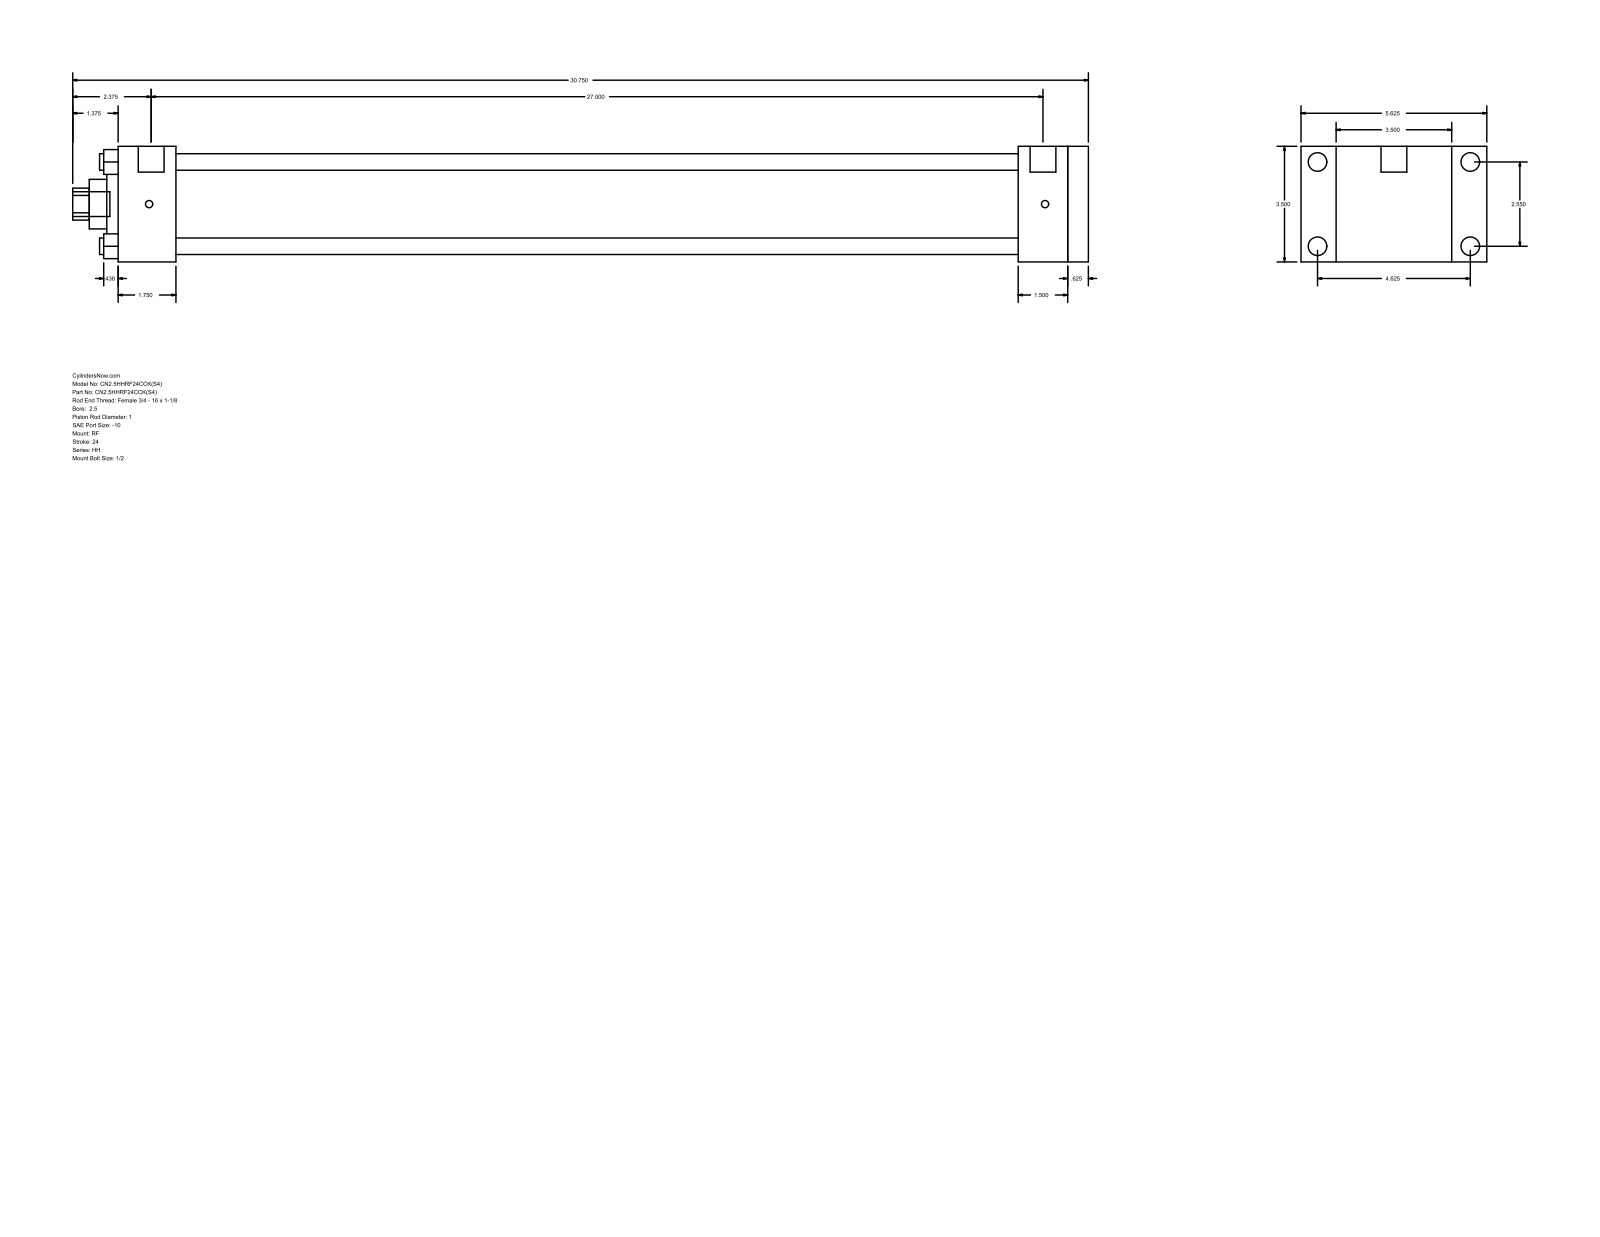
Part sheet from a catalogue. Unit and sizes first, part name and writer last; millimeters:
Units: millimetres
Overall size (bounding box): 781.05 × 142.88 × 88.9
Round holes (diameter × count): ⌀12.7 ×4, ⌀25.4 ×1, ⌀38.1 ×1, ⌀60.33 ×1, ⌀73.03 ×1
Round bosses / shafts (diameter × count): ⌀14.3 ×4, ⌀5.56 ×4, ⌀19.84 ×2, ⌀19.05 ×1
Partial cylindrical surfaces — rounded edges, fillets, slot ends (radius × count): R12.29 ×1
Main face-to-face distances: 88.9, 15.88, 730.25, 746.13, 44.46, 685.79, 701.67, 692.16, 647.7, 38.09
Hole centre spacings: 45.79, 64.76, 91.58
Bodies: 0 solids, 94 faces (65 planar, 29 cylindrical, 0 other)
Part name (STEP PRODUCT): HH_RF__0250_1
STEP written by: GSSL Pune (CONFIG_CONTROL_DESIGN)
